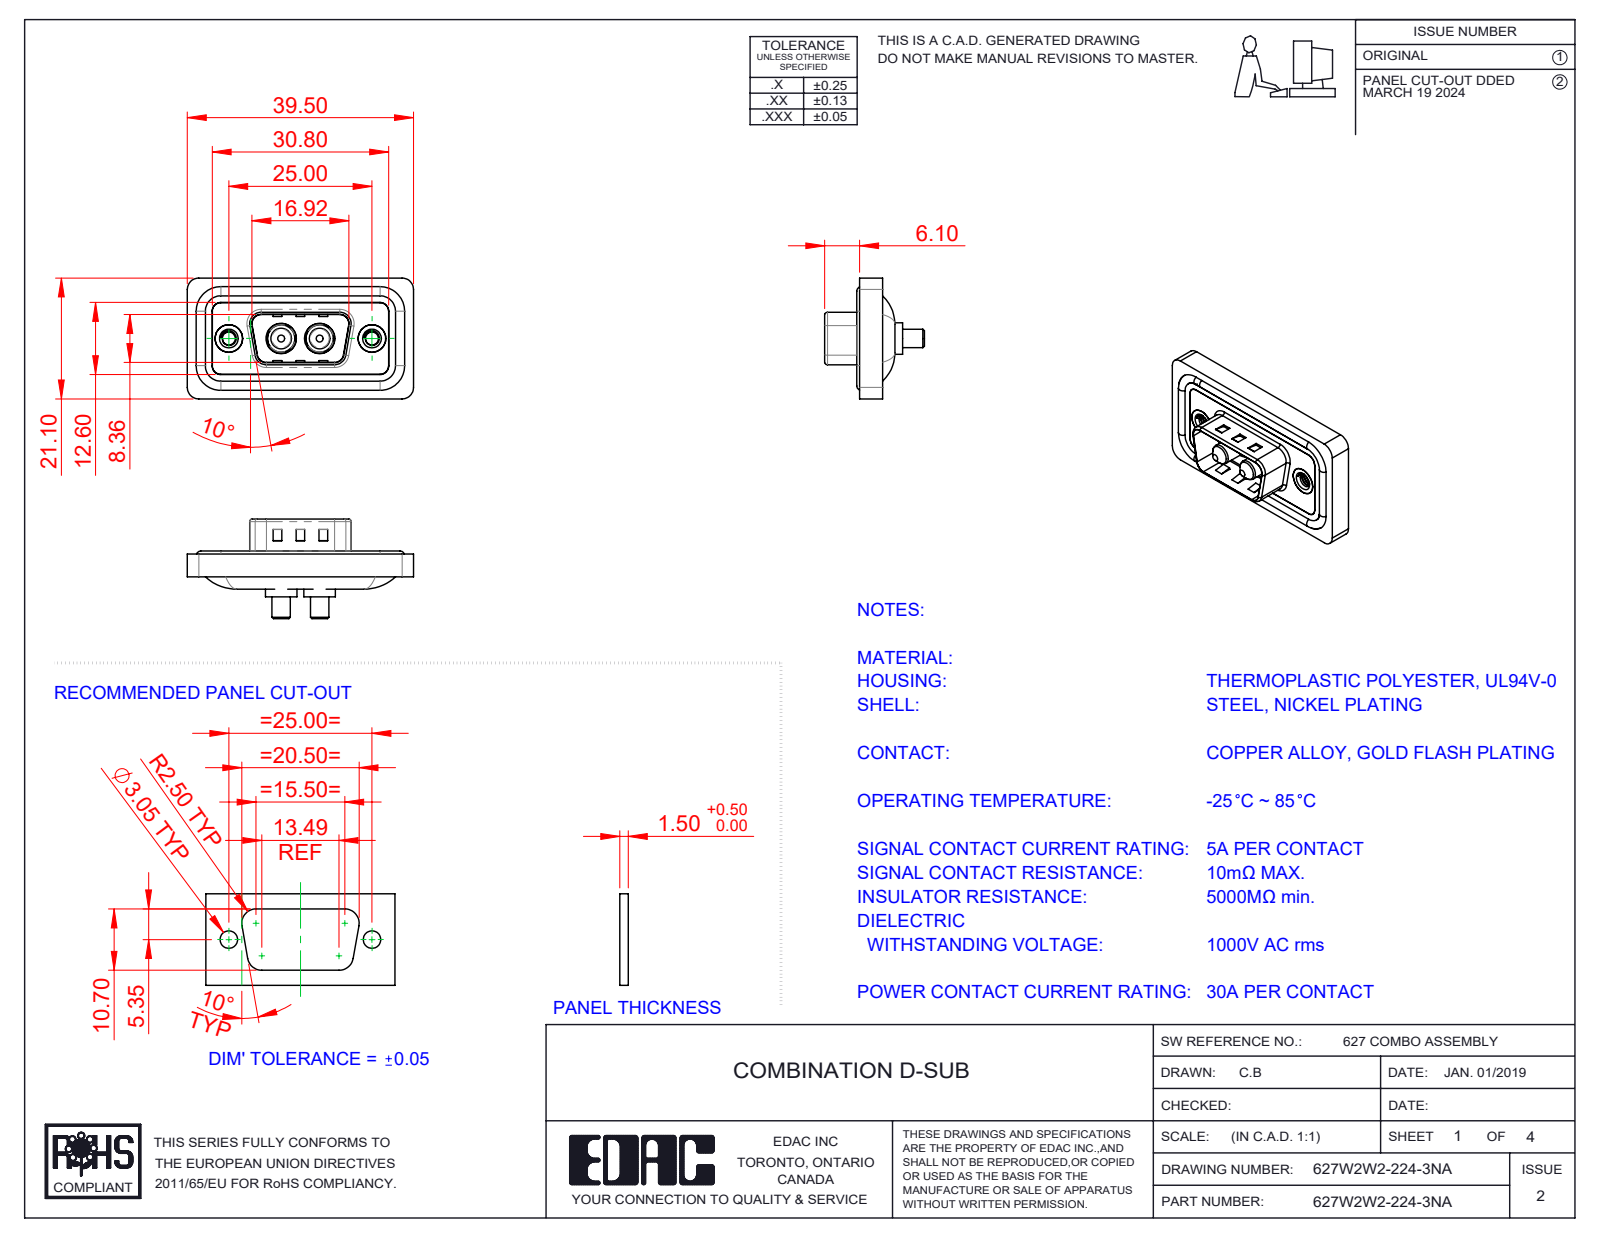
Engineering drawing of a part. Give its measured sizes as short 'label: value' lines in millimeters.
name: 627Combo Shell Front_09 Contacts; 627W2W2-224-3NA; 627Combo Housing_2W2; Power Pin_30A S (+3 more)
written by: SolidWorks 2023 (CONFIG_CONTROL_DESIGN)
unit: mm
bodies: 11 solids, 487 faces (165 planar, 220 cylindrical, 102 other)
size: 39.5 × 21.1 × 17.4
volume: 4 476 mm³; area: 6 991 mm²
holes: 2× ⌀2.26, 2× ⌀4, 2× ⌀4.8, 2× ⌀4.85, 2× ⌀5, 2× ⌀5.3
bosses: 4× ⌀1.6, 2× ⌀5.5, 2× ⌀5.2, 2× ⌀4.9, 2× ⌀4.75, 2× ⌀3.75, 2× ⌀3.6, 2× ⌀3.2
rounds: 22× R1.5, 18× R2, 8× R0.5, 8× R1.6, 4× R0.25, 4× R0.6, 4× R0.65, 4× R0.9
face distances: 0.4, 1.1, 2.9, 3.1, 0.5, 1.6, 1.5, 4, 2.5, 0.7
hole spacings: 9.14, 15.86, 6.72, 25
